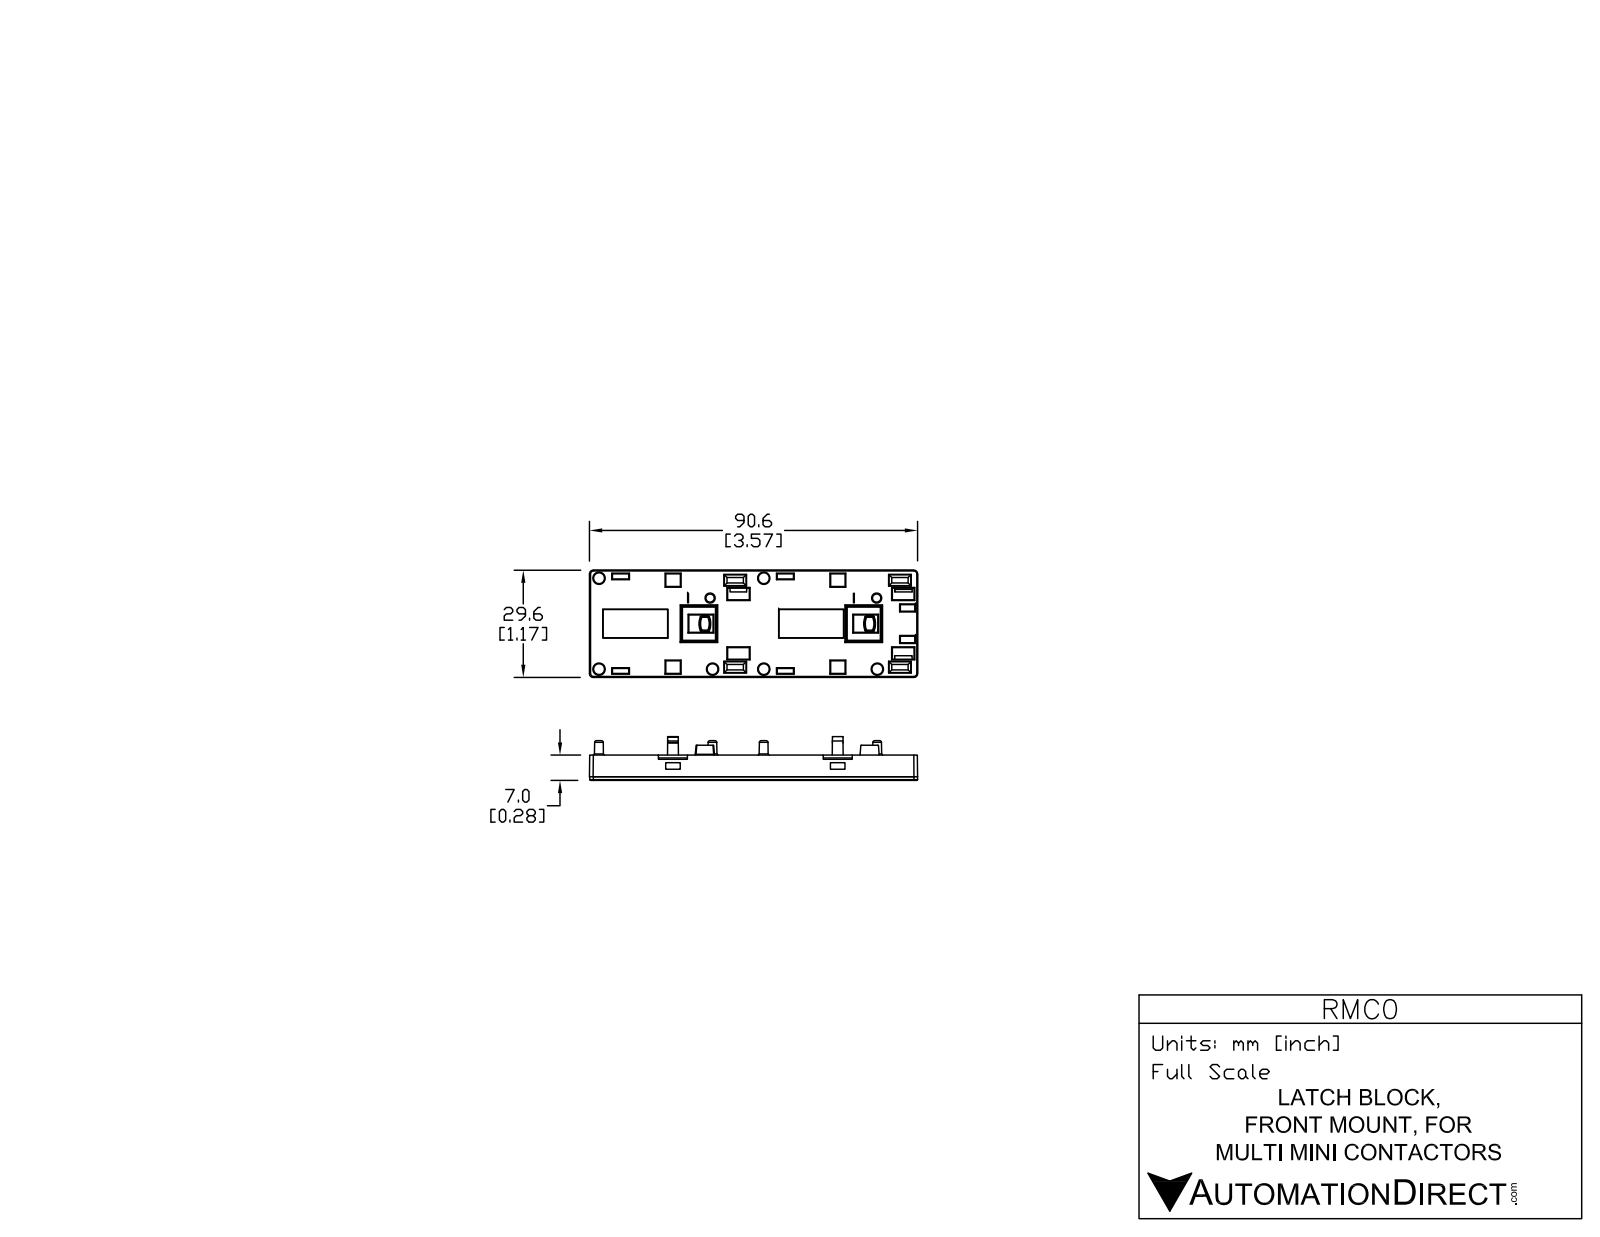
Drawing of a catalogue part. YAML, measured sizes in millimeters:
part_name: "RMC0"
step_written_by: "SolidWorks 2013 (AUTOMOTIVE_DESIGN)"
units: millimeters
bodies: {solids: 8, faces: 381, planar: 307, cylindrical: 44, other: 30}
overall_size: [90.6, 29.6, 12.1]
volume: 6864
surface_area: 14860
round_holes:
  - {diameter: 3, count: 6}
round_bosses_or_shafts:
  - {diameter: 2.49, count: 6}
partial_cylinders:
  - {radius: 0.17, count: 4}
  - {radius: 1, count: 4}
  - {radius: 0.5, count: 2}
  - {radius: 0.6, count: 2}
face_to_face_distances: [1, 6, 7, 5, 28.6, 29.6, 27.6, 3, 2, 1.25]
hole_center_spacings: [45.5, 25.1, 31.35, 40.16, 51.96, 14.15, 28.81, 76.85]
